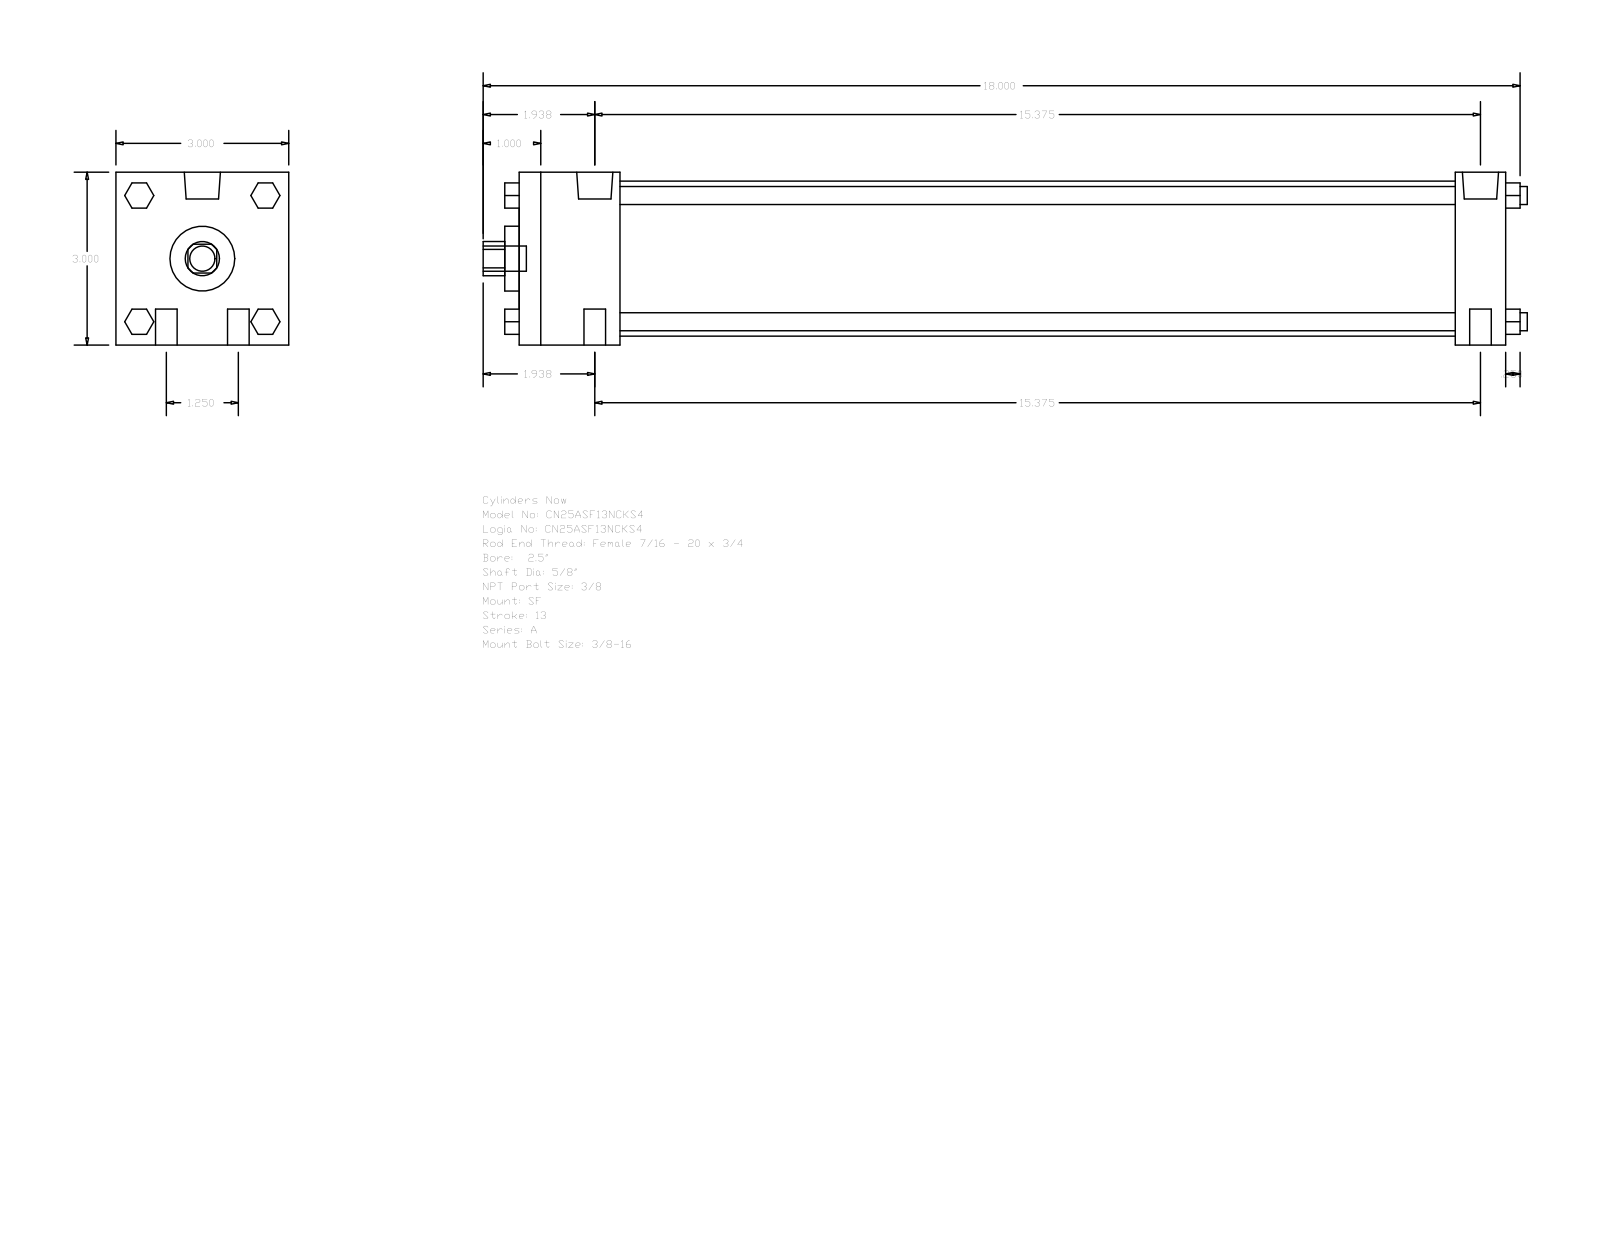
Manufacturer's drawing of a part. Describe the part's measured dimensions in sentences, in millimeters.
The part is named "A_SF__0250_0.625". Its 3-D file was written by "GSSL Pune (CONFIG_CONTROL_DESIGN)". It is 0 solids with 124 faces: 94 planar, 30 cylindrical and 0 other. Overall it measures 460.38 by 76.2 by 76.2 millimeters. Round holes: 1 of diameter 15.88, 1 of diameter 28.57, 1 of diameter 68.33. Round bosses or shafts: 4 of diameter 9.53, 4 of diameter 7.94, 2 of diameter 15.93, 2 of diameter 5.56, 1 of diameter 11.11. Partial cylindrical surfaces (rounded edges, fillets, slot ends): 1 of radius 7.54. The main face-to-face distances are 76.2, 434.97, 44.45, 412.74, 22.23, 368.29, 390.52, 6.35, 441.32, 50.8.
